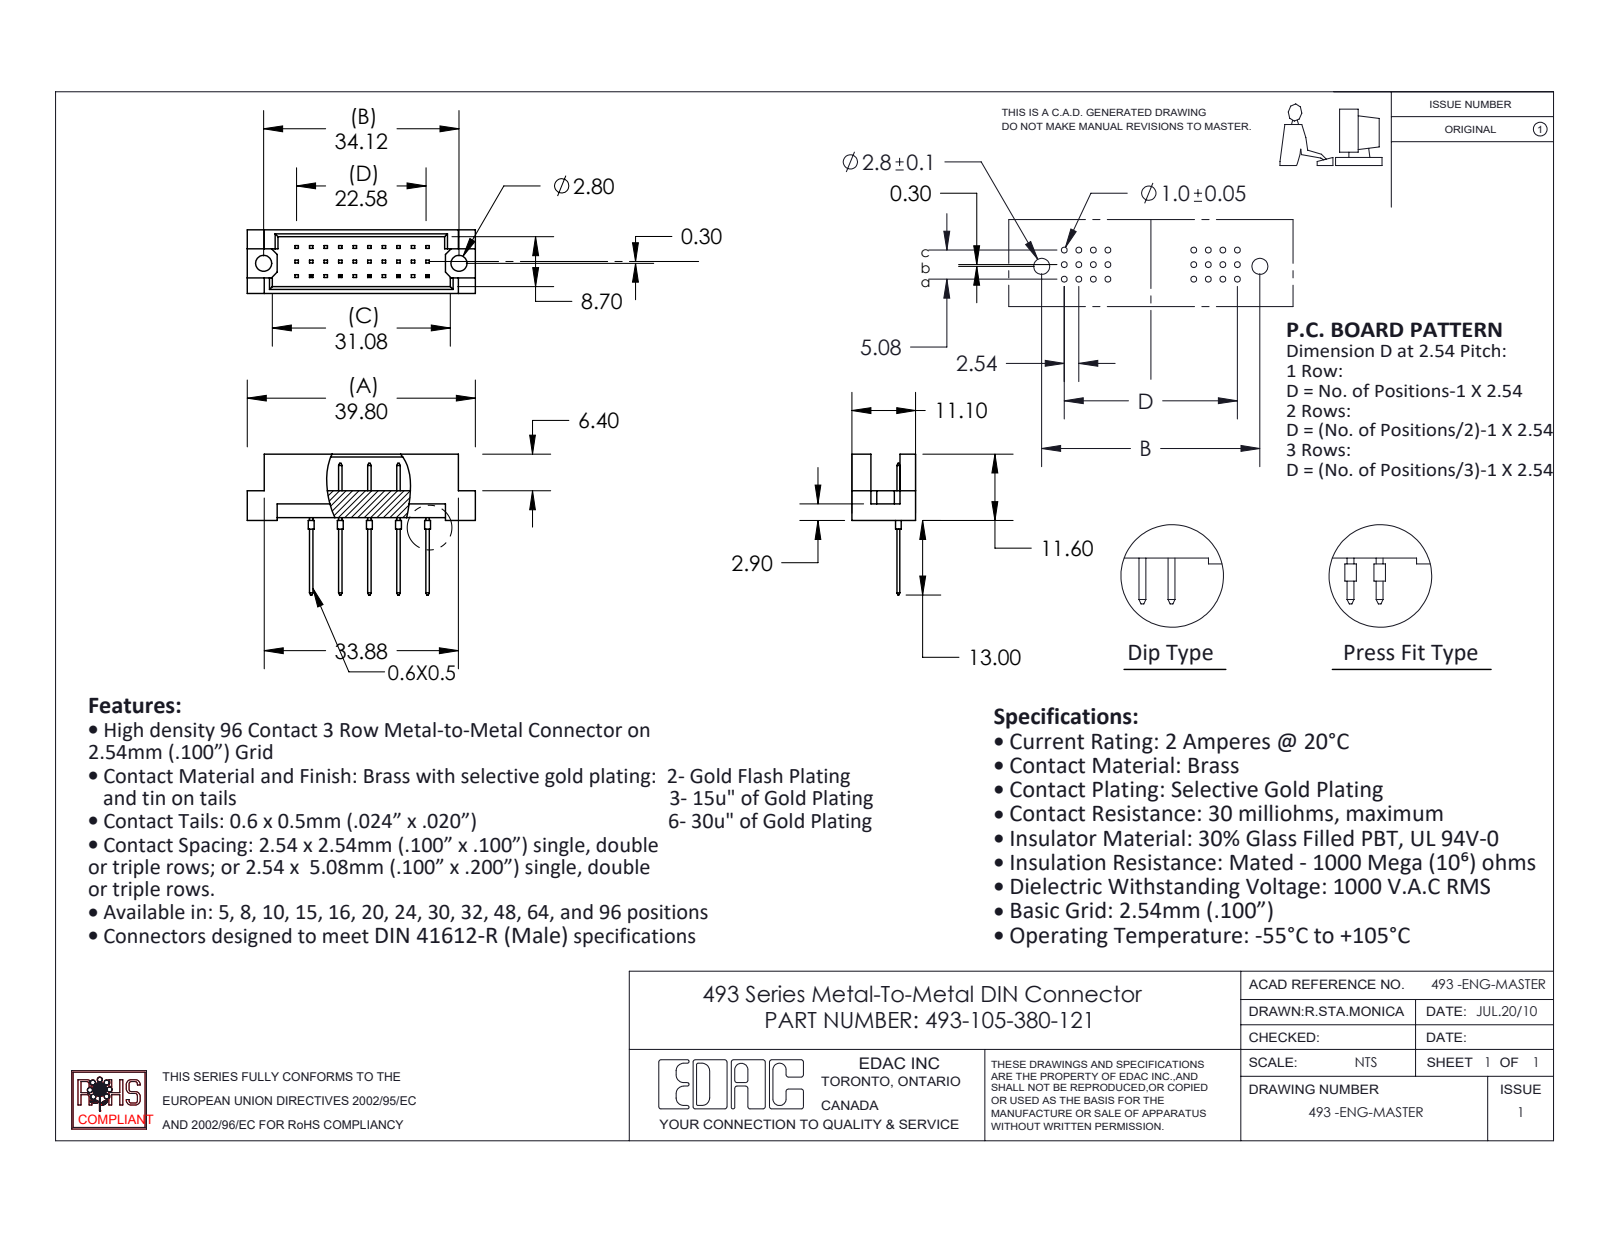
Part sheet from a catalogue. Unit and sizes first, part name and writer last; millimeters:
Units: millimetres
Overall size (bounding box): 39.8 × 24.6 × 11.1
Round holes (diameter × count): ⌀2.8 ×2
Round bosses / shafts (diameter × count): ⌀1 ×5
Main face-to-face distances: 1.2, 9.9, 11.1, 8.7, 0.5, 4.7, 5.08, 2.4, 2.76, 3.26
Hole centre spacings: 34.12
Volume: 2 411 mm³ · Surface area: 3 001 mm²
Bodies: 6 solids, 282 faces (268 planar, 14 cylindrical, 0 other)
Part name (STEP PRODUCT): 493-290_80; 493-105-380-121; 493 Part_30
STEP written by: SolidWorks 2020 (CONFIG_CONTROL_DESIGN)
